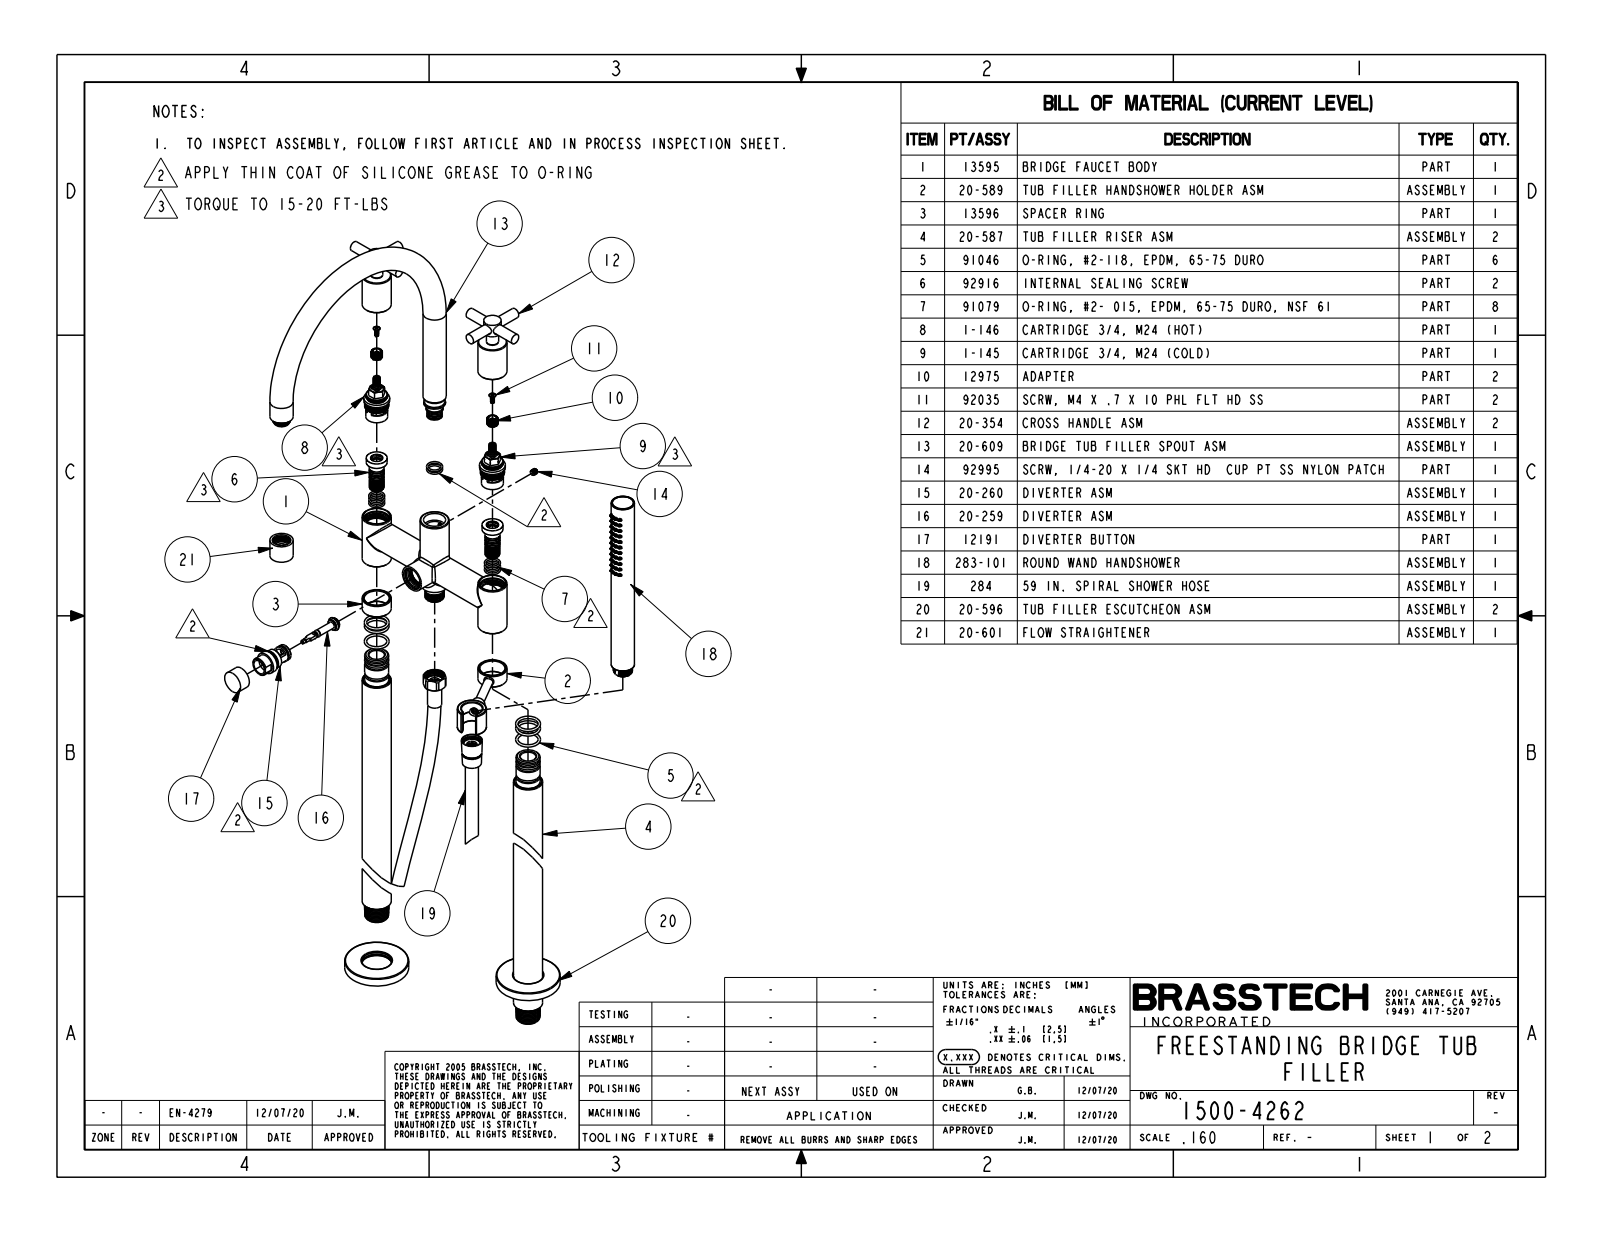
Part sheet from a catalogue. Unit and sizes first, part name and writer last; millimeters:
Units: millimetres
Overall size (bounding box): 1064.8 × 343.2 × 276.2
Round holes (diameter × count): ⌀3.6 ×44, ⌀3 ×1, ⌀15.4 ×1, ⌀17.6 ×1, ⌀22.5 ×1, ⌀23.9 ×1
Round bosses / shafts (diameter × count): ⌀31.8 ×5, ⌀25.4 ×3, ⌀19.1 ×3, ⌀14.2 ×3, ⌀11.3 ×3, ⌀69.9 ×2, ⌀29.2 ×2, ⌀13.3 ×2
Partial cylindrical surfaces — rounded edges, fillets, slot ends (radius × count): R0.8 ×6, R2.5 ×4, R7.6 ×1, R8.6 ×1, R9.3 ×1, R10.4 ×1, R11.4 ×1, R12.5 ×1
Main face-to-face distances: 9.7, 823.3, 813.7, 34.9, 852.1, 842.4, 28.7, 60.1, 824.4, 814.8
Hole centre spacings: 15.3, 8.5, 4.3, 22.5, 29.8, 14.7, 17.1, 7.4
Volume: 2 130 000 mm³ · Surface area: 336 600 mm²
Bodies: 4 solids, 1420 faces (221 planar, 466 cylindrical, 733 other)
Part name (STEP PRODUCT): 1500-4262
STEP written by: CREO PARAMETRIC BY PTC INC, 2019352 (CONFIG_CONTROL_DESIGN)
